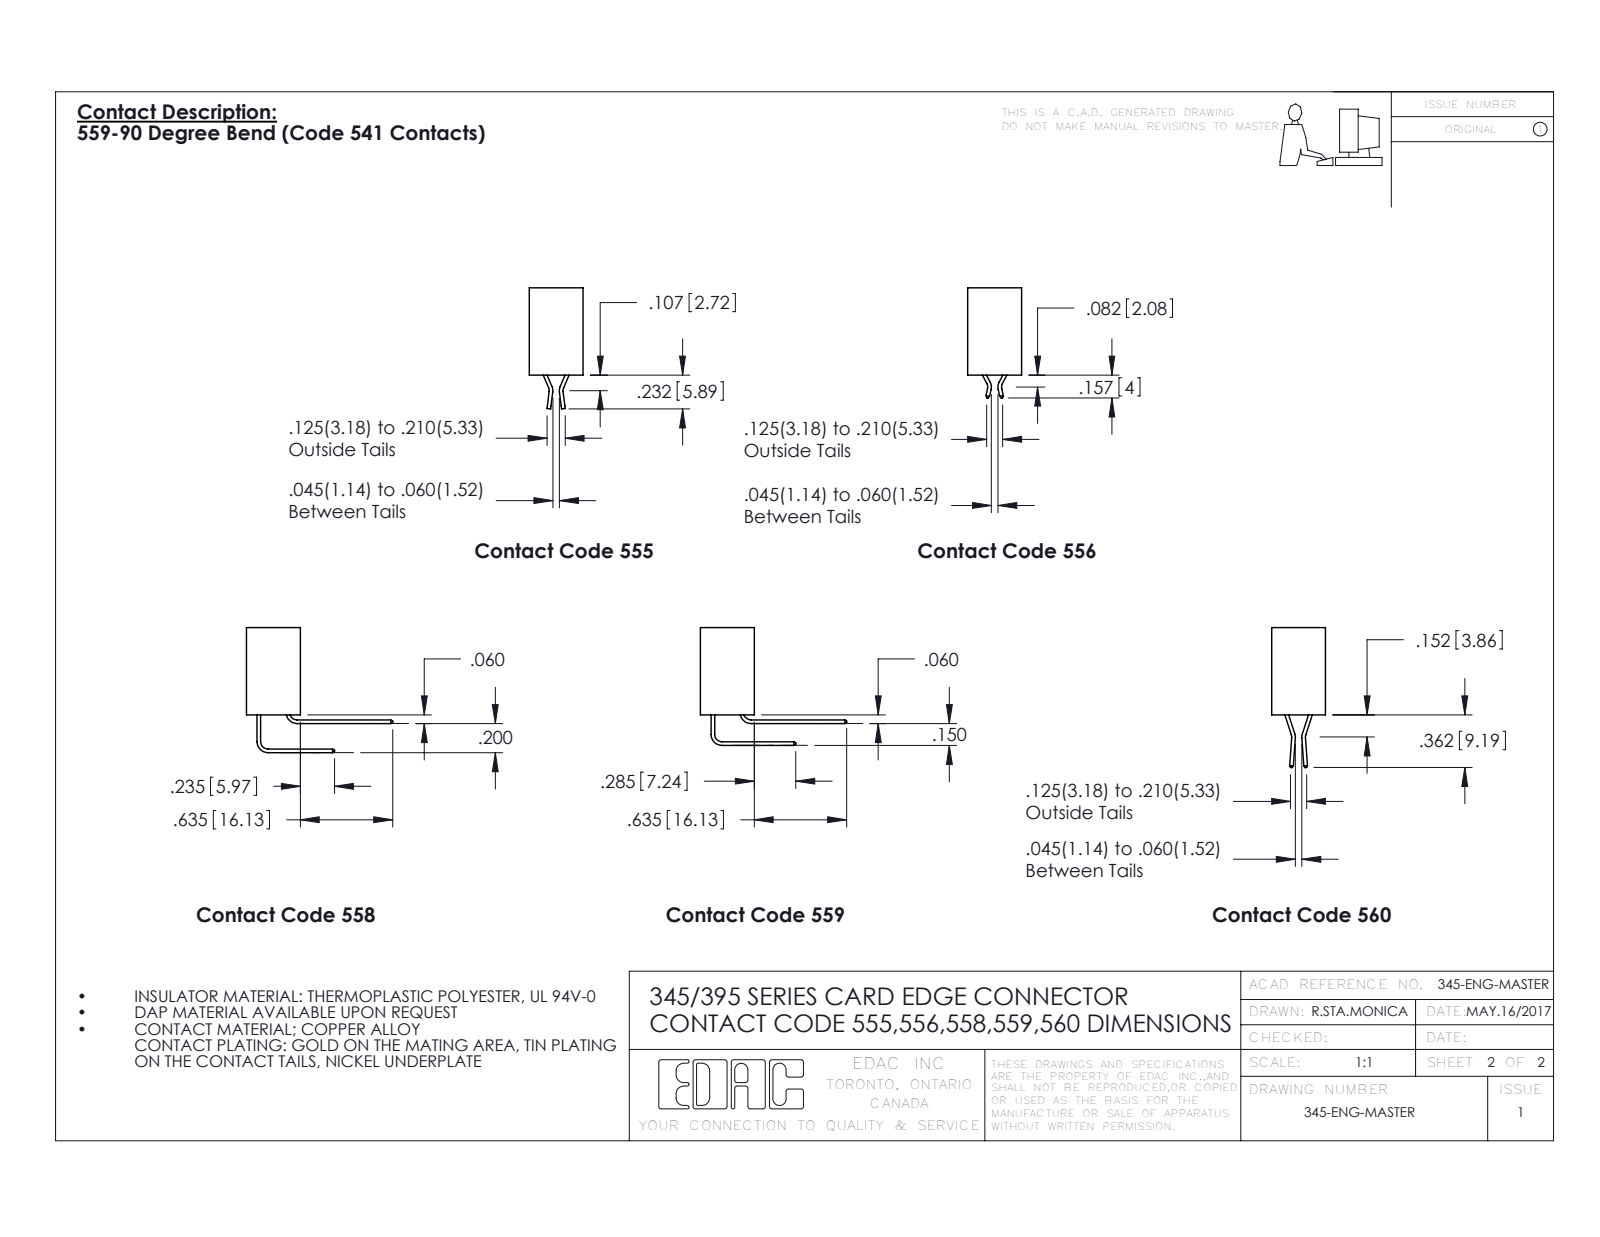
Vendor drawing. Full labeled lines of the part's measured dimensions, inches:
Part name (STEP PRODUCT): 345 Part_Flush Mounting Lugs - Side Mount; 395-013-559-112; 345-292-001_558 559 Tail - 1
STEP written by: SolidWorks 2016 (CONFIG_CONTROL_DESIGN)
Units: inches
Bodies: 14 solids, 906 faces (626 planar, 280 cylindrical, 0 other)
Overall size (bounding box): 2.135 × 1.005 × 0.659
Volume: 0.297 in³ · Surface area: 9.593 in²
Round holes (diameter × count): ⌀0.128 ×2, ⌀0.064 ×1
Partial cylindrical surfaces — rounded edges, fillets, slot ends (radius × count): R0.006 ×26, R0.01 ×22, R0.007 ×6, R0.031 ×6, R0.026 ×3, R0.031 ×2, R0.04 ×2, R0.014 ×1
Main face-to-face distances: 0.2, 0.298, 0.072, 0.37, 0.098, 0.272, 0.025, 0.1, 0.225, 0.05
Hole centre spacings: 1.875
